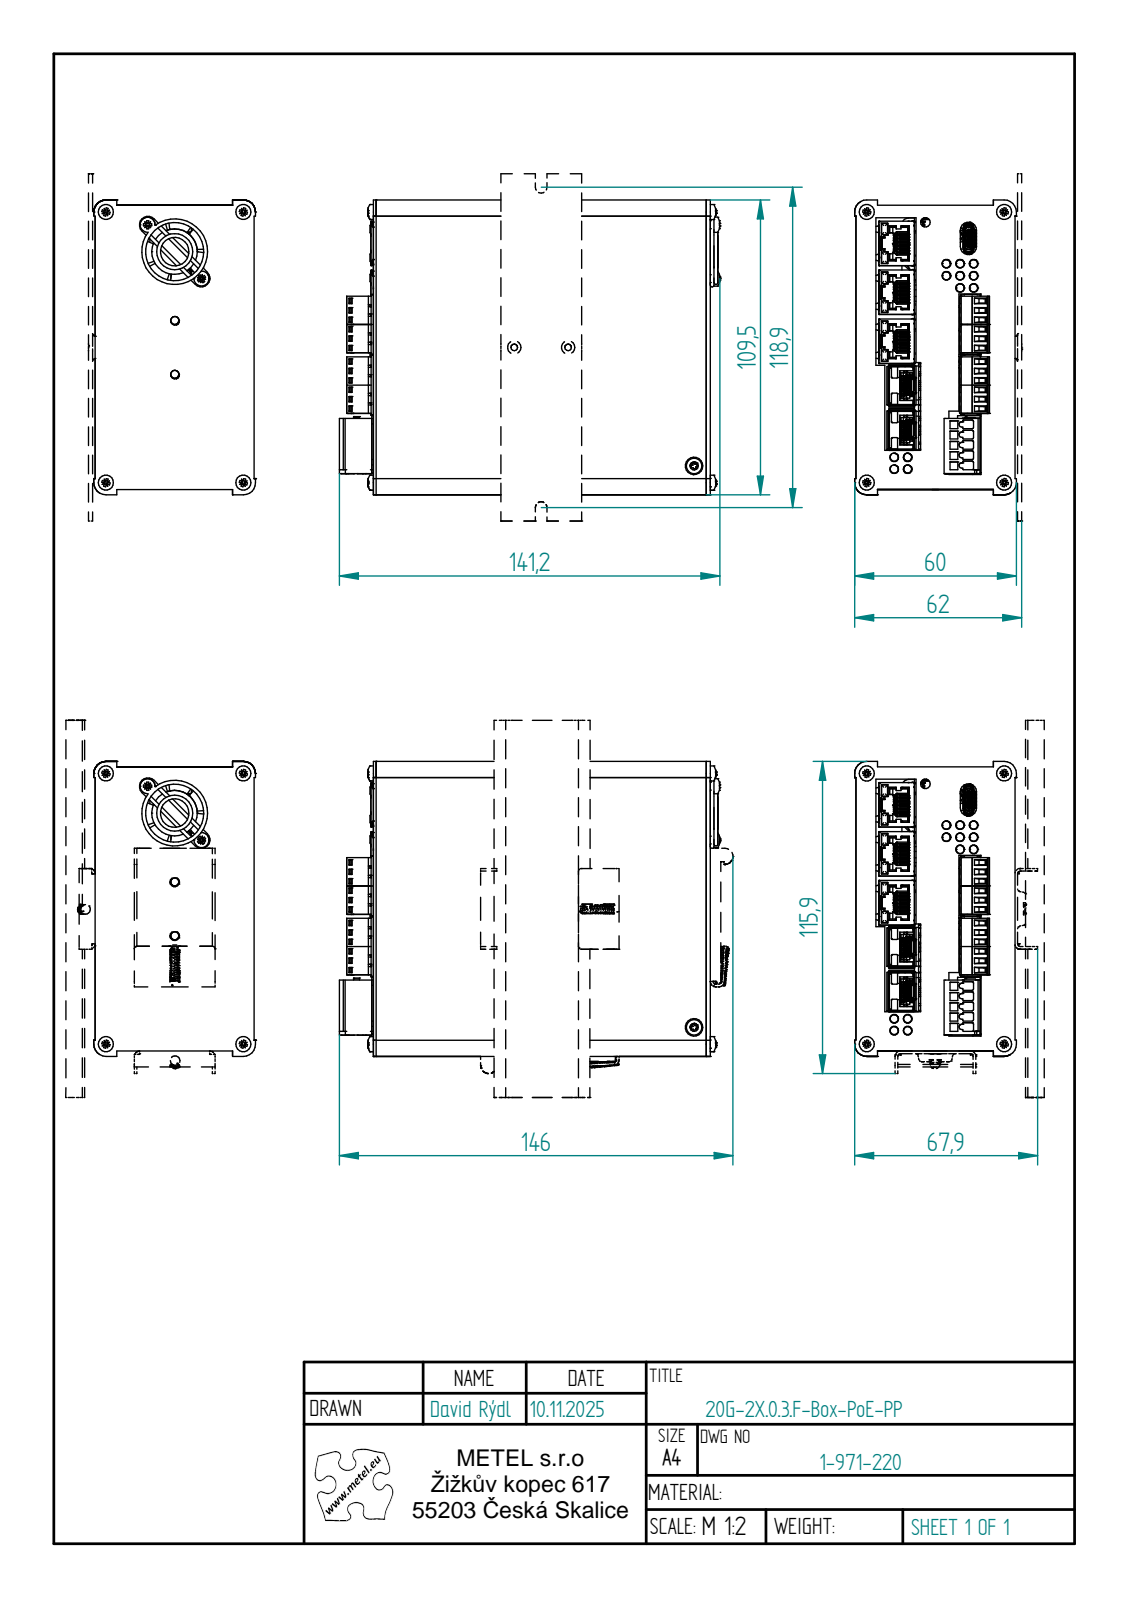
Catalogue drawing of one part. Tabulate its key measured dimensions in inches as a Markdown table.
| quantity | value |
| --- | --- |
| part name | 20G-2S.0.3_F_G; 20G-2X03_MAIN_UP2; S1_0; 4363x10458xx_0 (+8 more) |
| STEP written by | Solid Edge (AUTOMOTIVE_DESIGN) |
| units | inches |
| bodies | 133 solids, 15644 faces (11501 planar, 3294 cylindrical, 849 other) |
| overall size | 5.749 × 5.512 × 2.772 |
| volume | 9.642 in³ |
| surface area | 305.5 in² |
| round holes (diameter × count) | 0.059 × 17, 0.075 × 12, 0.083 × 12, 0.11 × 12, 0.128 × 12, 0.118 × 7, 0.138 × 7, 0.018 × 4, 0.097 × 4, 0.098 × 4, 0.106 × 4, 0.126 × 4 |
| round bosses / shafts (diameter × count) | 0.071 × 14, 0.118 × 12, 0.22 × 6, 0.114 × 6, 0.079 × 3, 0.07 × 2, 0.055 × 2, 0.024 × 2 |
| partial cylindrical surfaces (radius × count) | 0.004 × 157, 0.01 × 141, 0.008 × 92, 0.006 × 83, 0.01 × 78, 0.009 × 54, 0.039 × 50, 0.04 × 48 |
| main face-to-face distances | 0.059, 2.264, 0.039, 0.157, 2.323, 0.098, 3.996, 2.205, 2.362, 3.839 |
| hole center spacings | 0.787, 0.138, 0.266, 0.177, 0.199, 1.879, 2.58, 4.444 |
